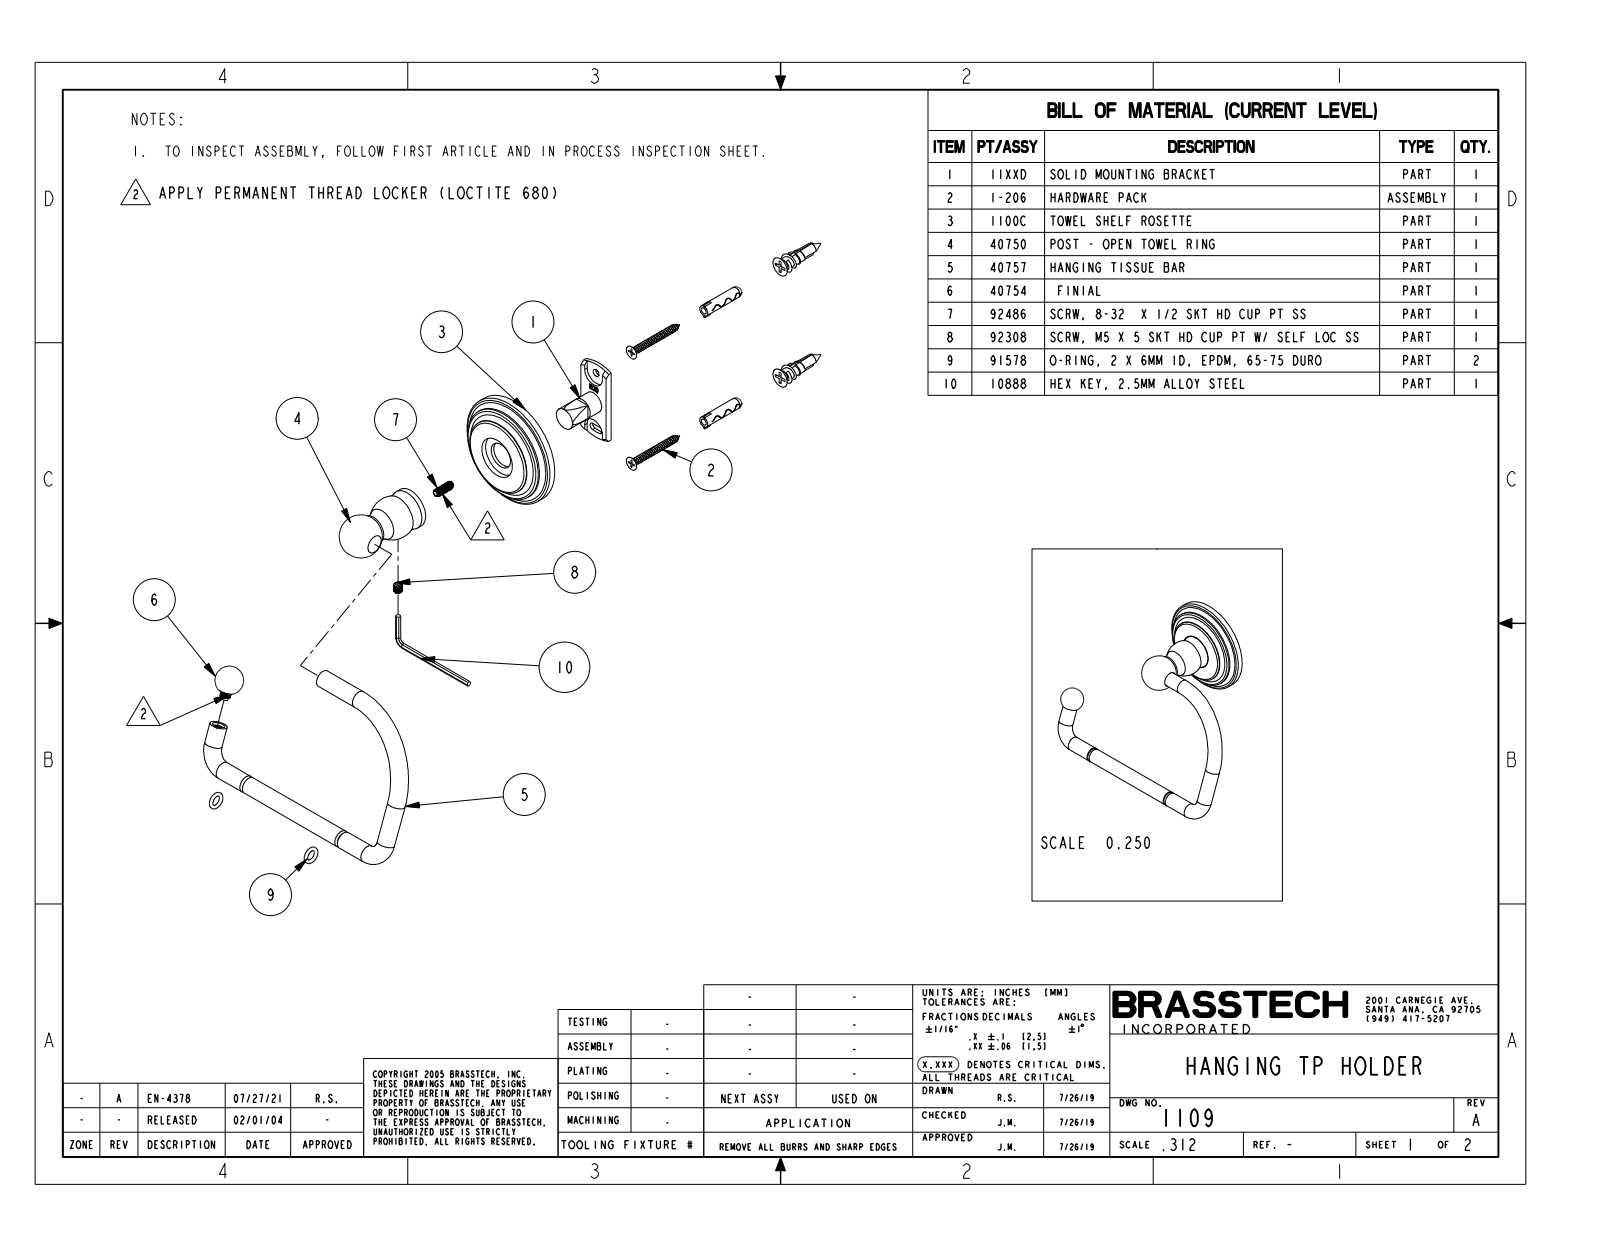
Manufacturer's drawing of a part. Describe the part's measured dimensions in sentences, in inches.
The part is named "1109". Its 3-D file was written by "CREO PARAMETRIC BY PTC INC, 2018400 (AUTOMOTIVE_DESIGN)". It is 1 solid with 68 faces: 7 planar, 21 cylindrical and 40 other. Overall it measures 5.878 by 4.437 by 3.221 inches. Its volume is 4.422 cubic inches and its surface area 33.01 square inches. Round holes: 1 of diameter 0.413. Round bosses or shafts: 4 of diameter 0.394, 1 of diameter 2.56, 1 of diameter 2.182, 1 of diameter 1.748. Partial cylindrical surfaces (rounded edges, fillets, slot ends): 1 of radius 0.086. The main face-to-face distances are 0.512, 0.362, 0.15, 0.189, 0.173, 0.323, 1.947, 1.758, 1.585, 1.435.
